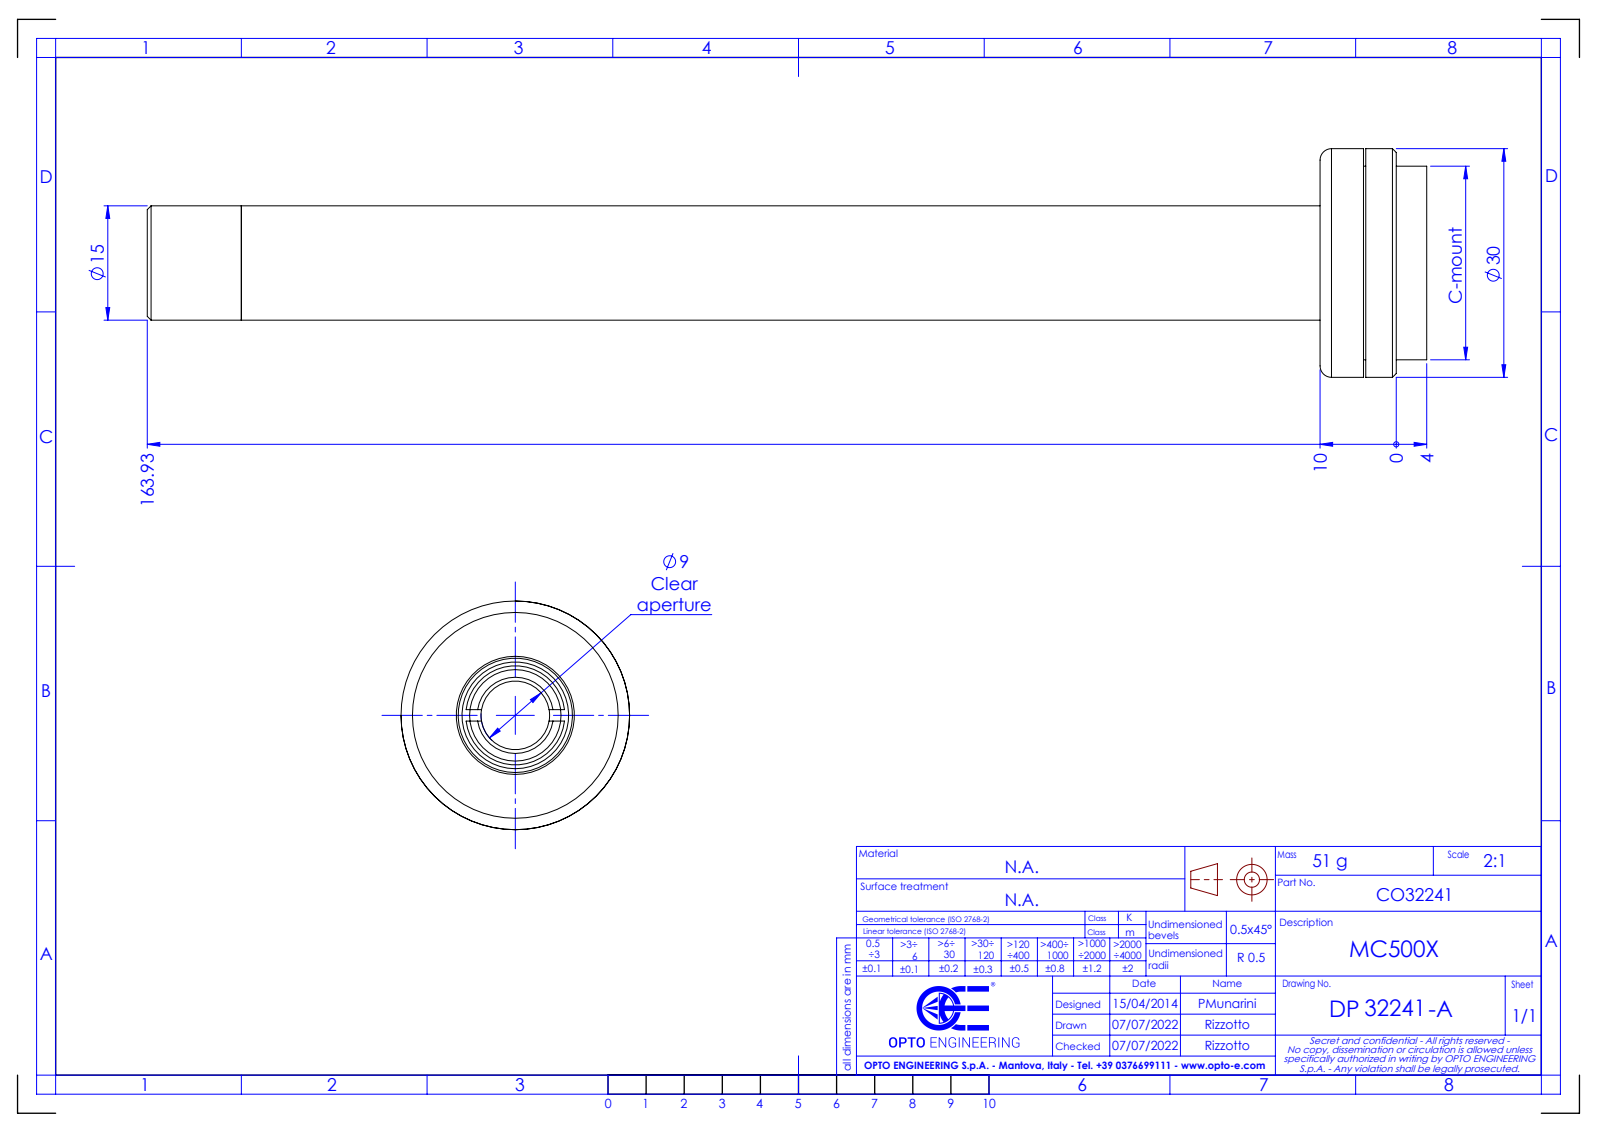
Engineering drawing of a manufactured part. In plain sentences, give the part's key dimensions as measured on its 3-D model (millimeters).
The part is named "DP32241-A_MC500X". Its 3-D file was written by "SolidWorks 2021 (CONFIG_CONTROL_DESIGN)". It is 0 solids with 49 faces: 16 planar, 18 cylindrical and 15 other. Overall it measures 167.93 by 30 by 30 millimeters. Round holes: 1 of diameter 9, 1 of diameter 12. Round bosses or shafts: 1 of diameter 30, 1 of diameter 25.4, 1 of diameter 15, 1 of diameter 14.5. The main face-to-face distances are 4, 6, 5.7, 10, 4.3, 14, 8.3, 8, 153.93, 159.63.
